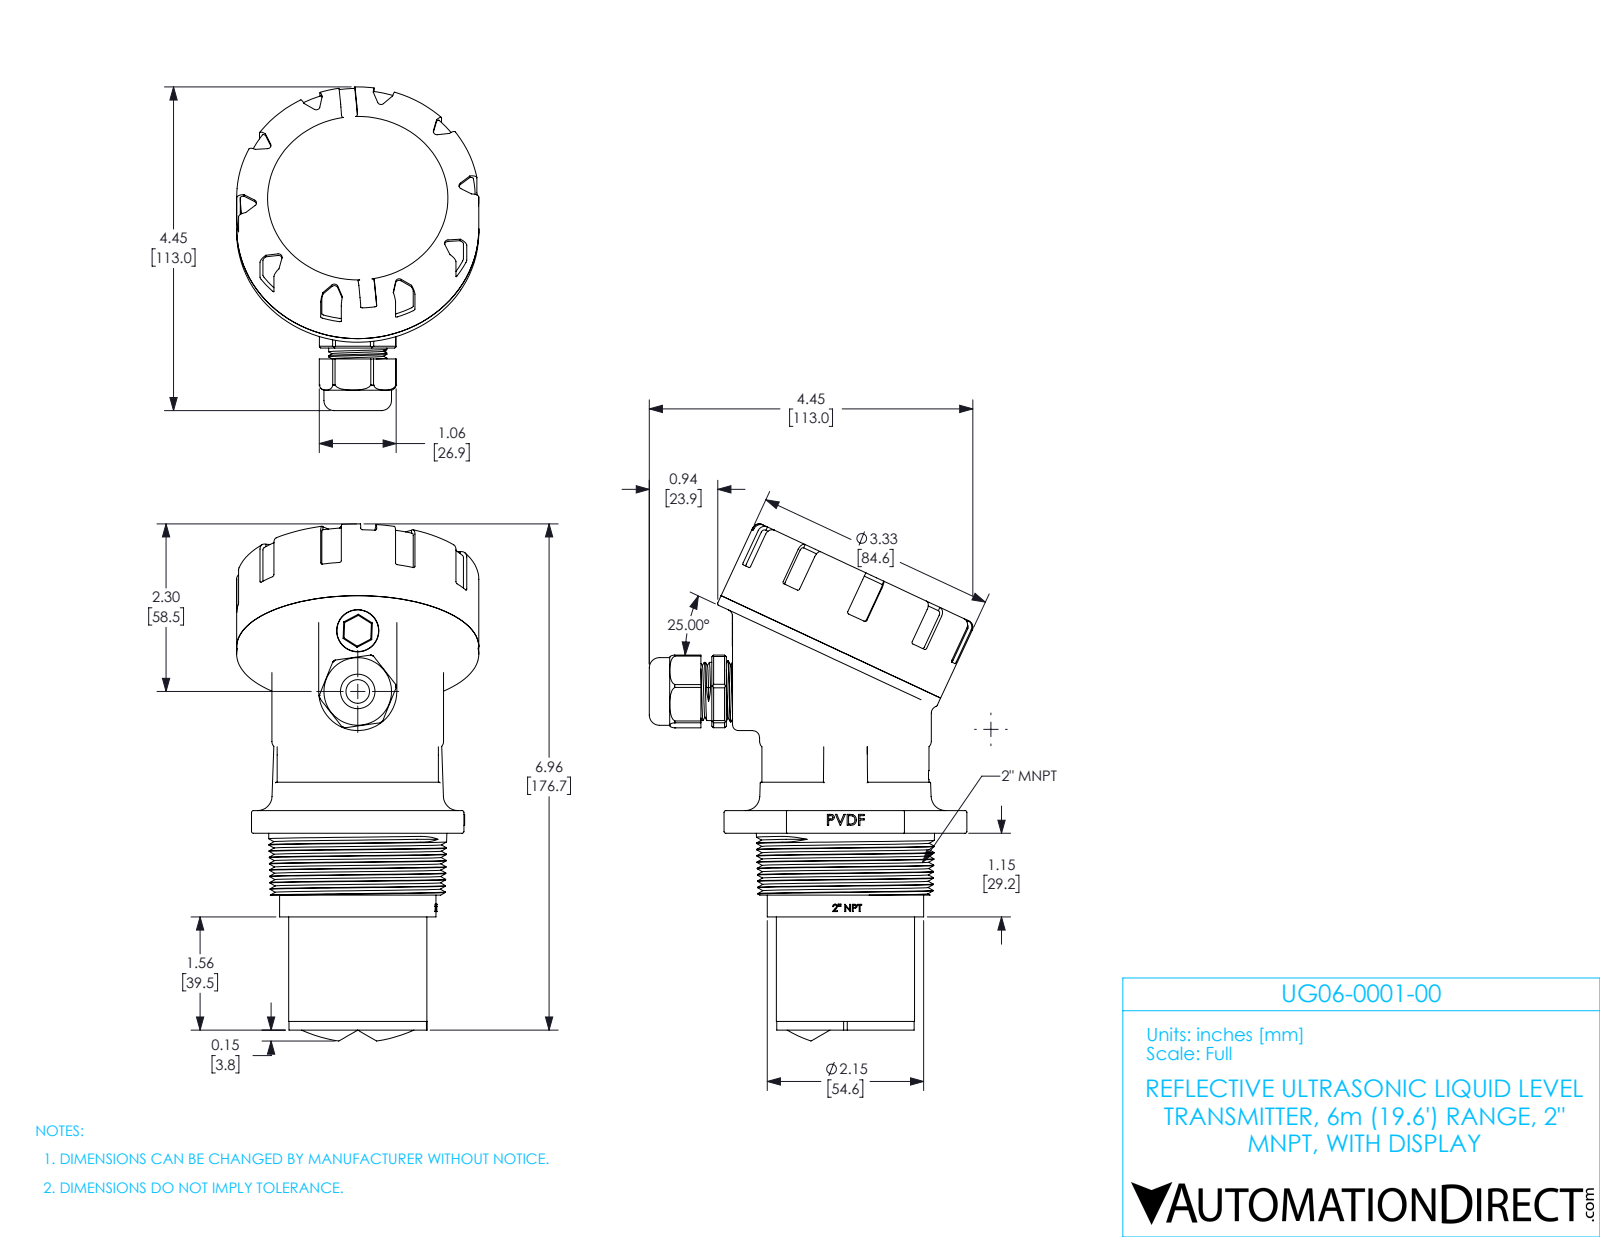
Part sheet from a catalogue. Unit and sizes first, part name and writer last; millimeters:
Units: millimetres
Overall size (bounding box): 180.5 × 113 × 84.6
Round holes (diameter × count): ⌀3.3 ×4, ⌀5 ×1, ⌀8.3 ×1, ⌀12.1 ×1, ⌀13.2 ×1, ⌀18.8 ×1, ⌀21.6 ×1, ⌀23.7 ×1, ⌀34.5 ×1, ⌀52 ×1, ⌀69 ×1, ⌀72.4 ×1
Round bosses / shafts (diameter × count): ⌀84.6 ×2, ⌀76.2 ×1, ⌀71.8 ×1, ⌀70.4 ×1, ⌀59.9 ×1, ⌀58.3 ×1, ⌀54.6 ×1, ⌀48.3 ×1
Partial cylindrical surfaces — rounded edges, fillets, slot ends (radius × count): R1.3 ×27, R0.6 ×26, R0.8 ×14, R2.5 ×13, R1.7 ×6, R1.6 ×4, R2 ×2, R7.7 ×2
Main face-to-face distances: 1.3, 2.5, 6.7, 7.9, 1.7, 4.2, 1.7, 26.3, 4.2, 2.3
Hole centre spacings: 25.9, 16.5, 20, 21.2, 33, 40
Volume: 225 200 mm³ · Surface area: 147 700 mm²
Bodies: 9 solids, 1173 faces (602 planar, 317 cylindrical, 254 other)
Part name (STEP PRODUCT): UG06-0001-00 b2b
STEP written by: SolidWorks 2017 (AUTOMOTIVE_DESIGN)
